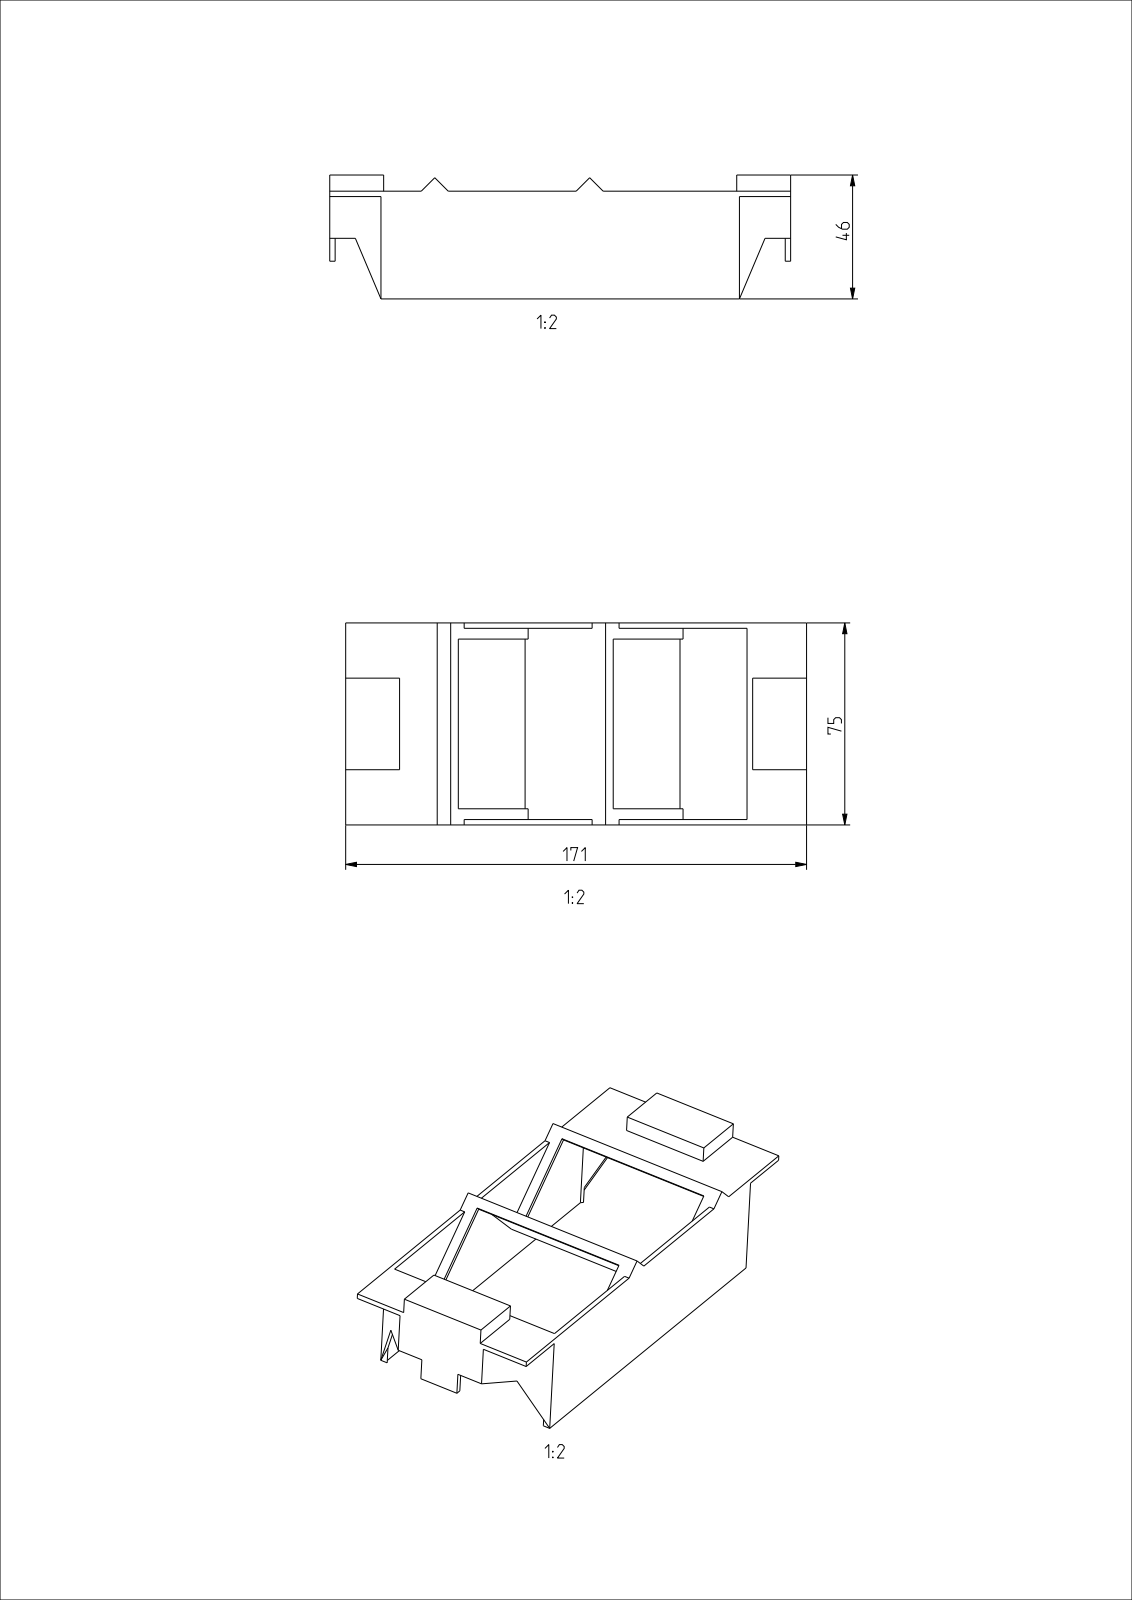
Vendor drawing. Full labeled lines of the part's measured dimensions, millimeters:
Part name (STEP PRODUCT): GTVD200KUN
STEP written by: CREO PARAMETRIC BY PTC INC, 2022024 (AUTOMOTIVE_DESIGN)
Units: millimetres
Bodies: 1 solid, 82 faces (82 planar, 0 cylindrical, 0 other)
Overall size (bounding box): 171 × 75 × 46
Volume: 55 687 mm³ · Surface area: 53 719 mm²
Main face-to-face distances: 2, 73, 40.63, 1.6, 75, 71, 42.23, 39.03, 145.05, 6
